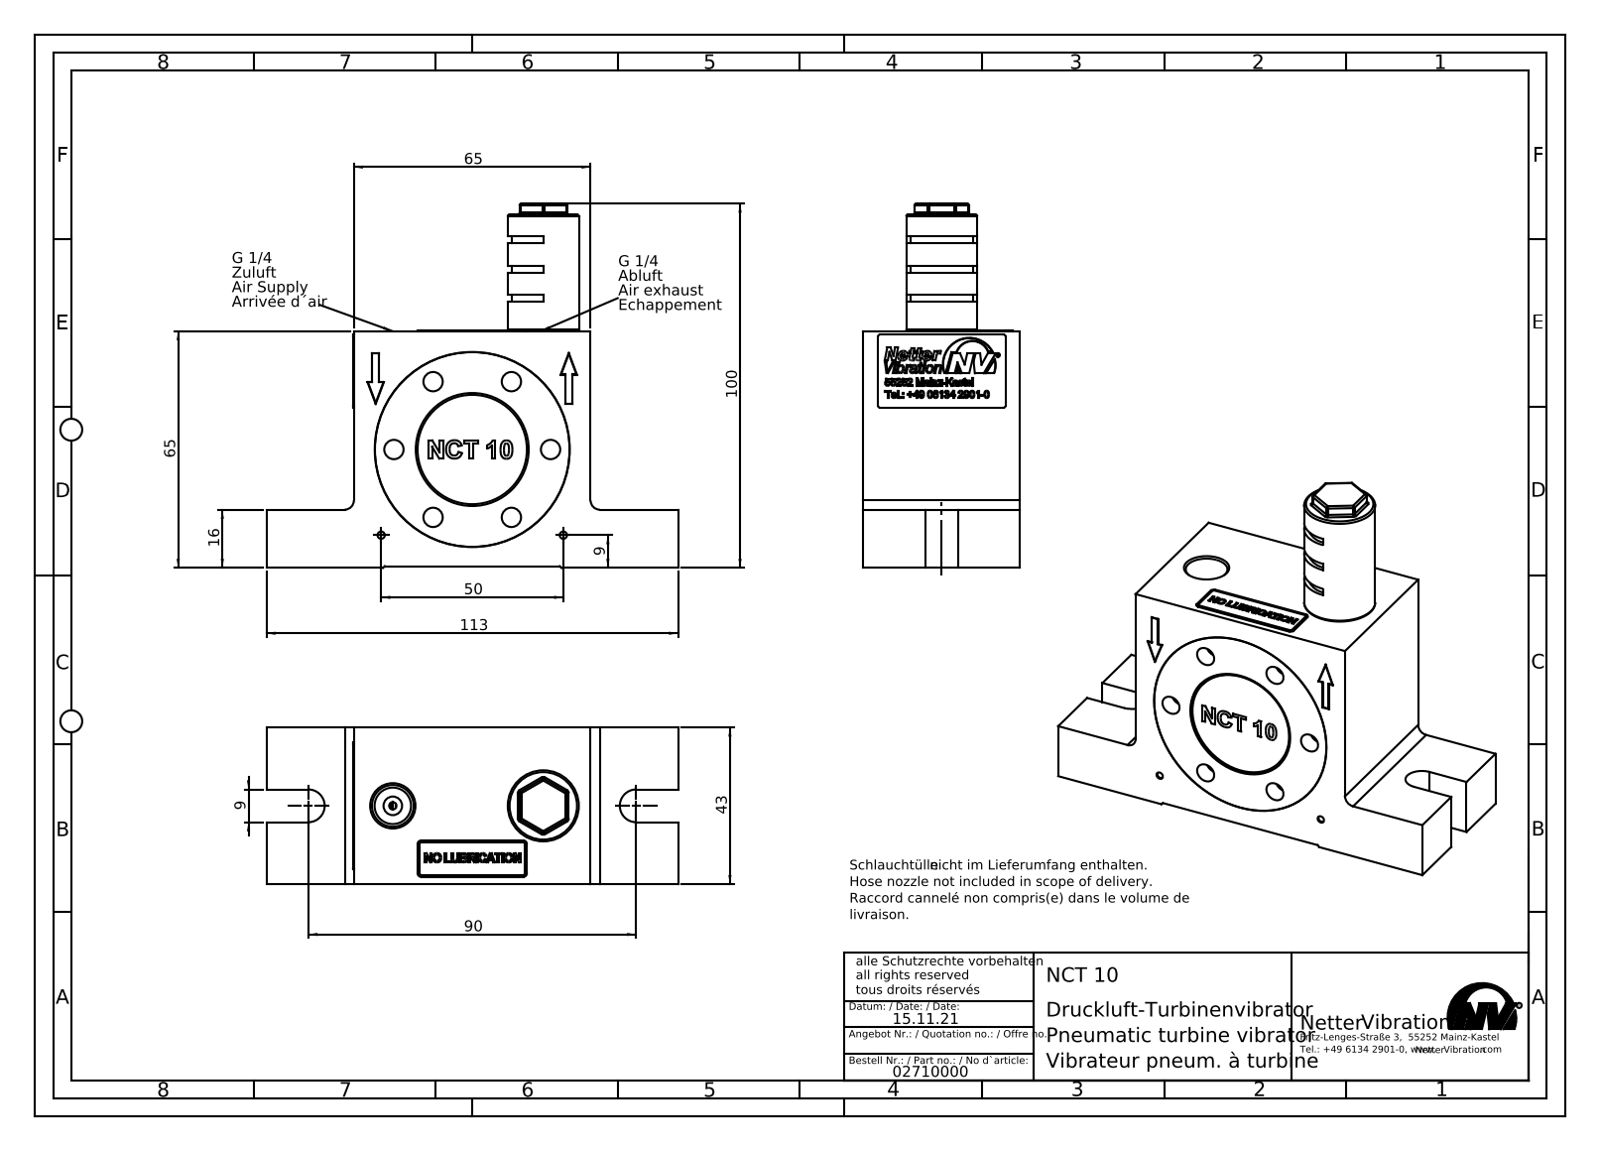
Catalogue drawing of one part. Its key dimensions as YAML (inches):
part_name: "NCT 10 Turbinenvibrator #02710000"
step_written_by: "SolidWorks 2015 (AUTOMOTIVE_DESIGN)"
units: inches
bodies: {solids: 6, faces: 328, planar: 204, cylindrical: 71, other: 53}
overall_size: [4.449, 3.937, 1.693]
volume: 13.8
surface_area: 64.14
round_holes:
  - {diameter: 0.209, count: 6}
  - {diameter: 0.079, count: 2}
  - {diameter: 0.451, count: 2}
  - {diameter: 1.22, count: 1}
  - {diameter: 2.063, count: 1}
round_bosses_or_shafts:
  - {diameter: 2.126, count: 1}
  - {diameter: 2.026, count: 1}
  - {diameter: 1.181, count: 1}
  - {diameter: 0.768, count: 1}
  - {diameter: 0.518, count: 1}
partial_cylinders:
  - {radius: 0.02, count: 22}
  - {radius: 0.039, count: 4}
  - {radius: 0.098, count: 2}
  - {radius: 0.177, count: 2}
  - {radius: 0.335, count: 1}
face_to_face_distances: [2.559, 1.693, 0.02, 0.315, 1.378, 0.157, 1.22, 2.539, 0.472, 0.63]
hole_center_spacings: [0.846, 1.466, 1.693, 0.593, 0.935, 1.351, 1.42, 1.751]
